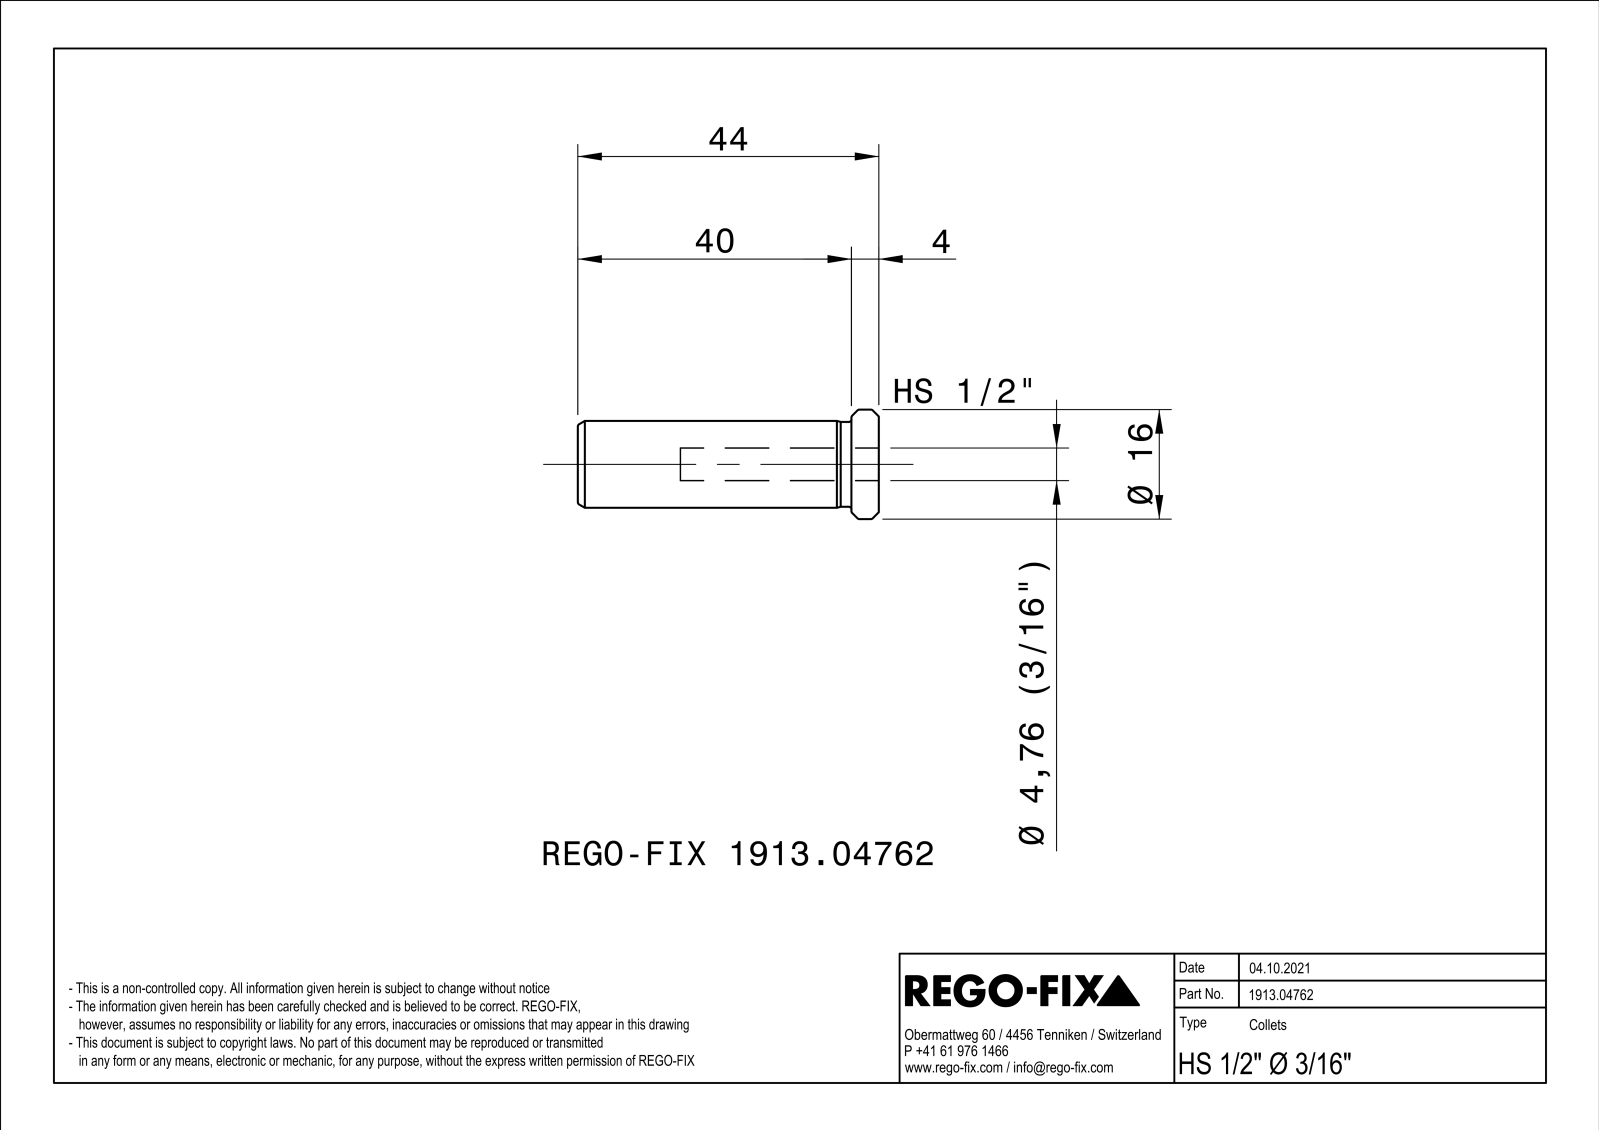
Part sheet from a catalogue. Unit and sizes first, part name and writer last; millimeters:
Units: millimetres
Overall size (bounding box): 44 × 15.98 × 15.98
Round holes (diameter × count): ⌀4.76 ×1, ⌀7.5 ×1
Round bosses / shafts (diameter × count): ⌀16 ×1, ⌀12.7 ×1, ⌀12.4 ×1
Main face-to-face distances: 0.8, 44, 4, 40
Volume: 4 330 mm³ · Surface area: 3 536 mm²
Bodies: 1 solid, 70 faces (22 planar, 11 cylindrical, 37 other)
Part name (STEP PRODUCT): NOCUT
STEP written by: SIEMENS PLM Software Solid Edge ST10 (AUTOMOTIVE_DESIGN)
